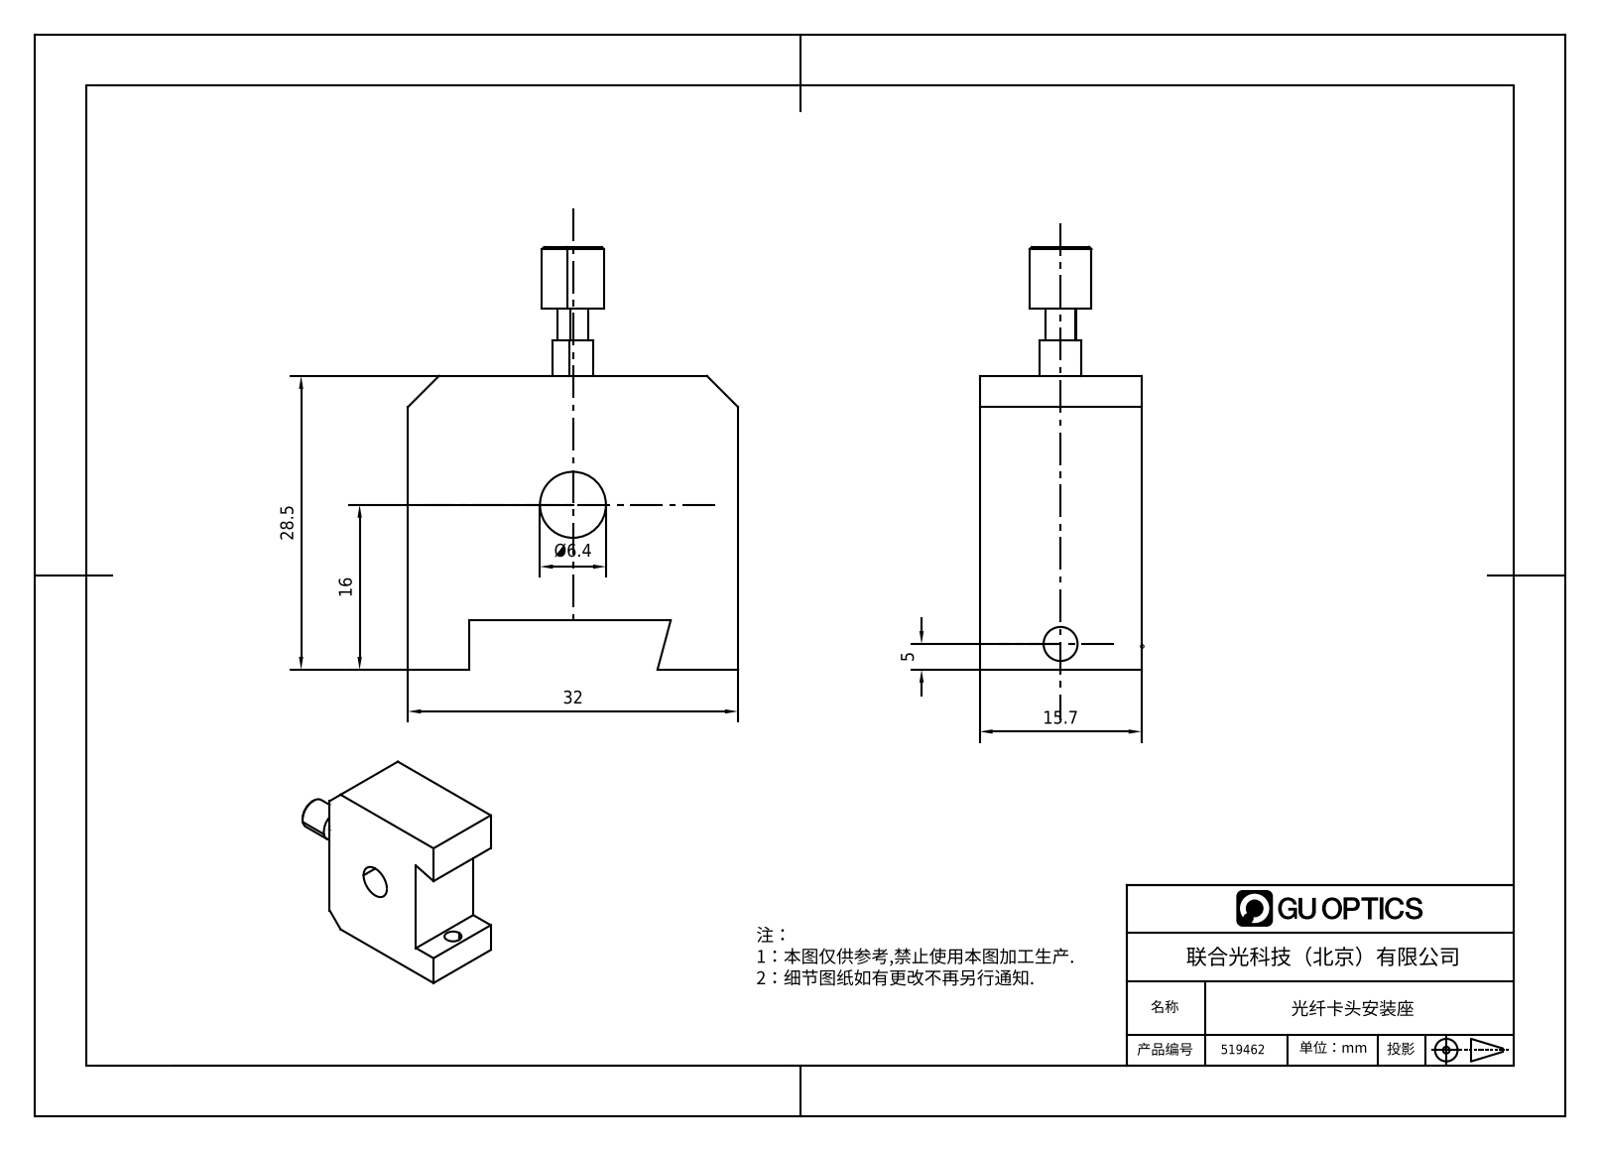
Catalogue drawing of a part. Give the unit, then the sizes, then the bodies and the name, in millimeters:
Units: millimetres
Overall size (bounding box): 41 × 32 × 15.7
Round holes (diameter × count): ⌀3.3 ×2, ⌀6.4 ×1
Round bosses / shafts (diameter × count): ⌀6 ×1, ⌀4 ×1, ⌀3 ×1
Main face-to-face distances: 15.7, 32, 23.7, 28.5, 4.8, 5.9, 26.1, 12.5, 36.2, 41
Volume: 12 455 mm³ · Surface area: 4 376 mm²
Bodies: 2 solids, 30 faces (16 planar, 12 cylindrical, 2 other)
Part name (STEP PRODUCT): MF-FC
STEP written by: SolidWorks 2016 (CONFIG_CONTROL_DESIGN)
